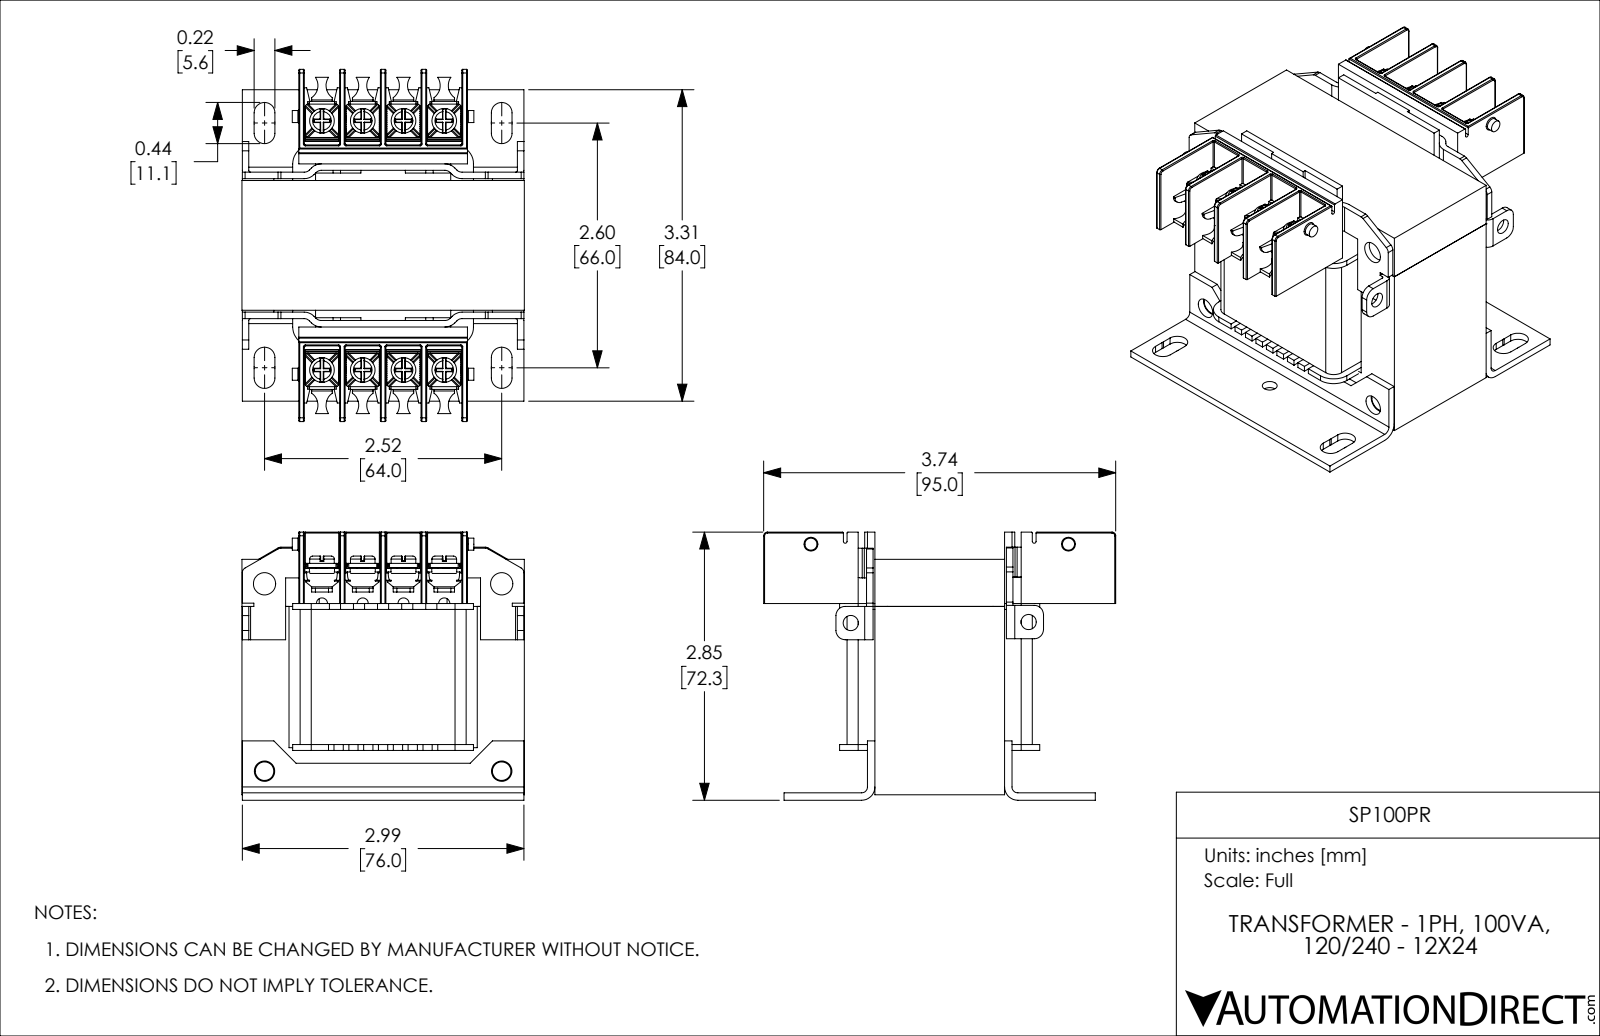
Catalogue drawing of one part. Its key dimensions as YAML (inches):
part_name: "SP100PR"
step_written_by: "SolidWorks 2018 (AUTOMOTIVE_DESIGN)"
units: inches
bodies: {solids: 41, faces: 3158, planar: 1936, cylindrical: 931, other: 291}
overall_size: [3.74, 3, 2.847]
volume: 13.95
surface_area: 138
round_holes:
  - {diameter: 0.157, count: 10}
  - {diameter: 0.105, count: 8}
  - {diameter: 0.138, count: 8}
  - {diameter: 0.236, count: 4}
  - {diameter: 0.161, count: 2}
  - {diameter: 0.197, count: 2}
  - {diameter: 0.217, count: 2}
round_bosses_or_shafts:
  - {diameter: 0.262, count: 8}
  - {diameter: 0.24, count: 8}
  - {diameter: 0.168, count: 8}
  - {diameter: 0.11, count: 8}
  - {diameter: 0.128, count: 3}
partial_cylinders:
  - {radius: 0.005, count: 52}
  - {radius: 0.01, count: 52}
  - {radius: 0.012, count: 40}
  - {radius: 0.029, count: 32}
  - {radius: 0.059, count: 22}
  - {radius: 0.157, count: 16}
  - {radius: 0.035, count: 12}
  - {radius: 0.079, count: 10}
face_to_face_distances: [0.5, 2, 0.059, 2.5, 1.378, 0.433, 0.079, 0.02, 0.118, 1]
hole_center_spacings: [0.433, 0.866, 2.671, 1.299, 2.636, 2.774, 2.661, 2.681]
